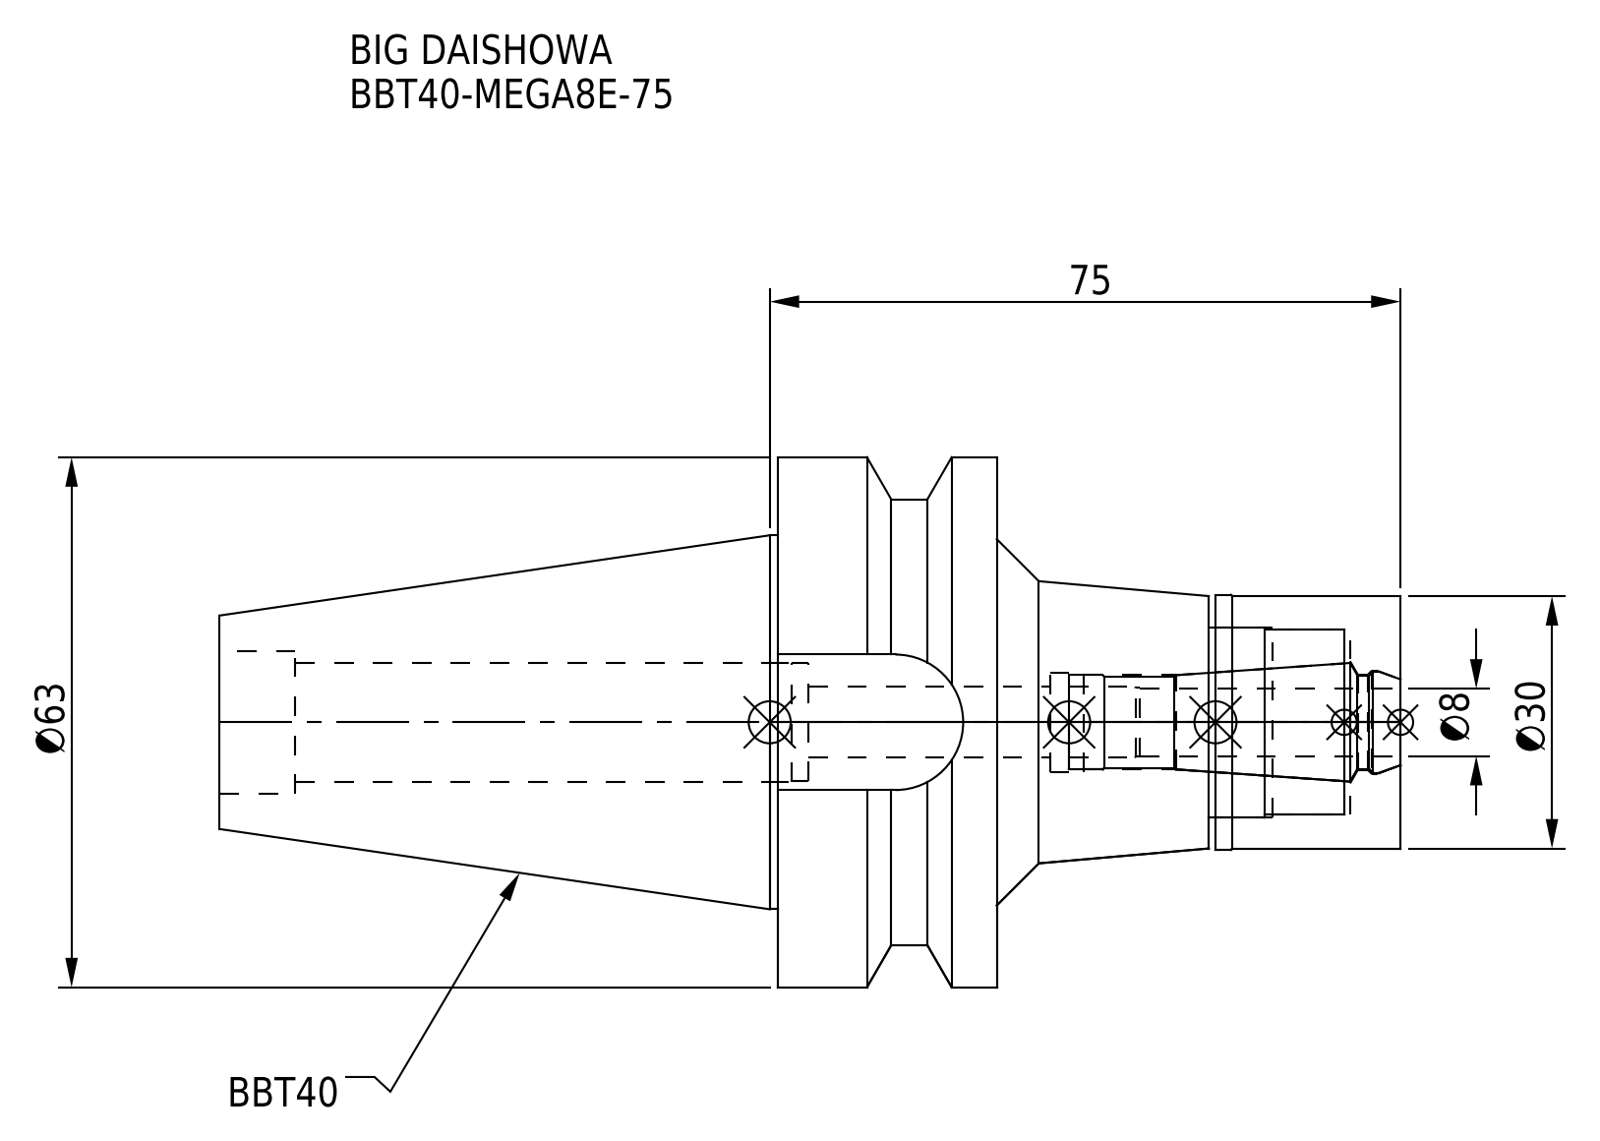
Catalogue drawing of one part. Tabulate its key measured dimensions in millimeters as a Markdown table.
| quantity | value |
| --- | --- |
| part name | BBT40-MEGA8E-75_1.stp; BBT40-MEGA8E-75-080.stp; MEN8_1.stp; DXF_TEMP_ASSY_ASM_4_ASM.stp (+3 more) |
| STEP written by | SolidWorks 2019 (CONFIG_CONTROL_DESIGN) |
| units | millimeters |
| bodies | 2 solids, 81 faces (21 planar, 40 cylindrical, 20 other) |
| overall size | 140.4 × 63 × 63 |
| volume | 155 127 mm³ |
| surface area | 31 824 mm² |
| round holes (diameter × count) | 8.4 × 1, 11.2 × 1, 11.4 × 1, 11.8 × 1, 12.3 × 1, 14 × 1, 14.2 × 1, 17 × 1, 22 × 1, 22.5 × 1 |
| round bosses / shafts (diameter × count) | 63 × 1, 53 × 1, 44.45 × 1, 30.3 × 1, 30 × 1 |
| partial cylindrical surfaces (radius × count) | 8.05 × 1 |
| main face-to-face distances | 26, 48, 74, 16.1, 45, 22, 52, 22.8, 0.8, 25.2 |
